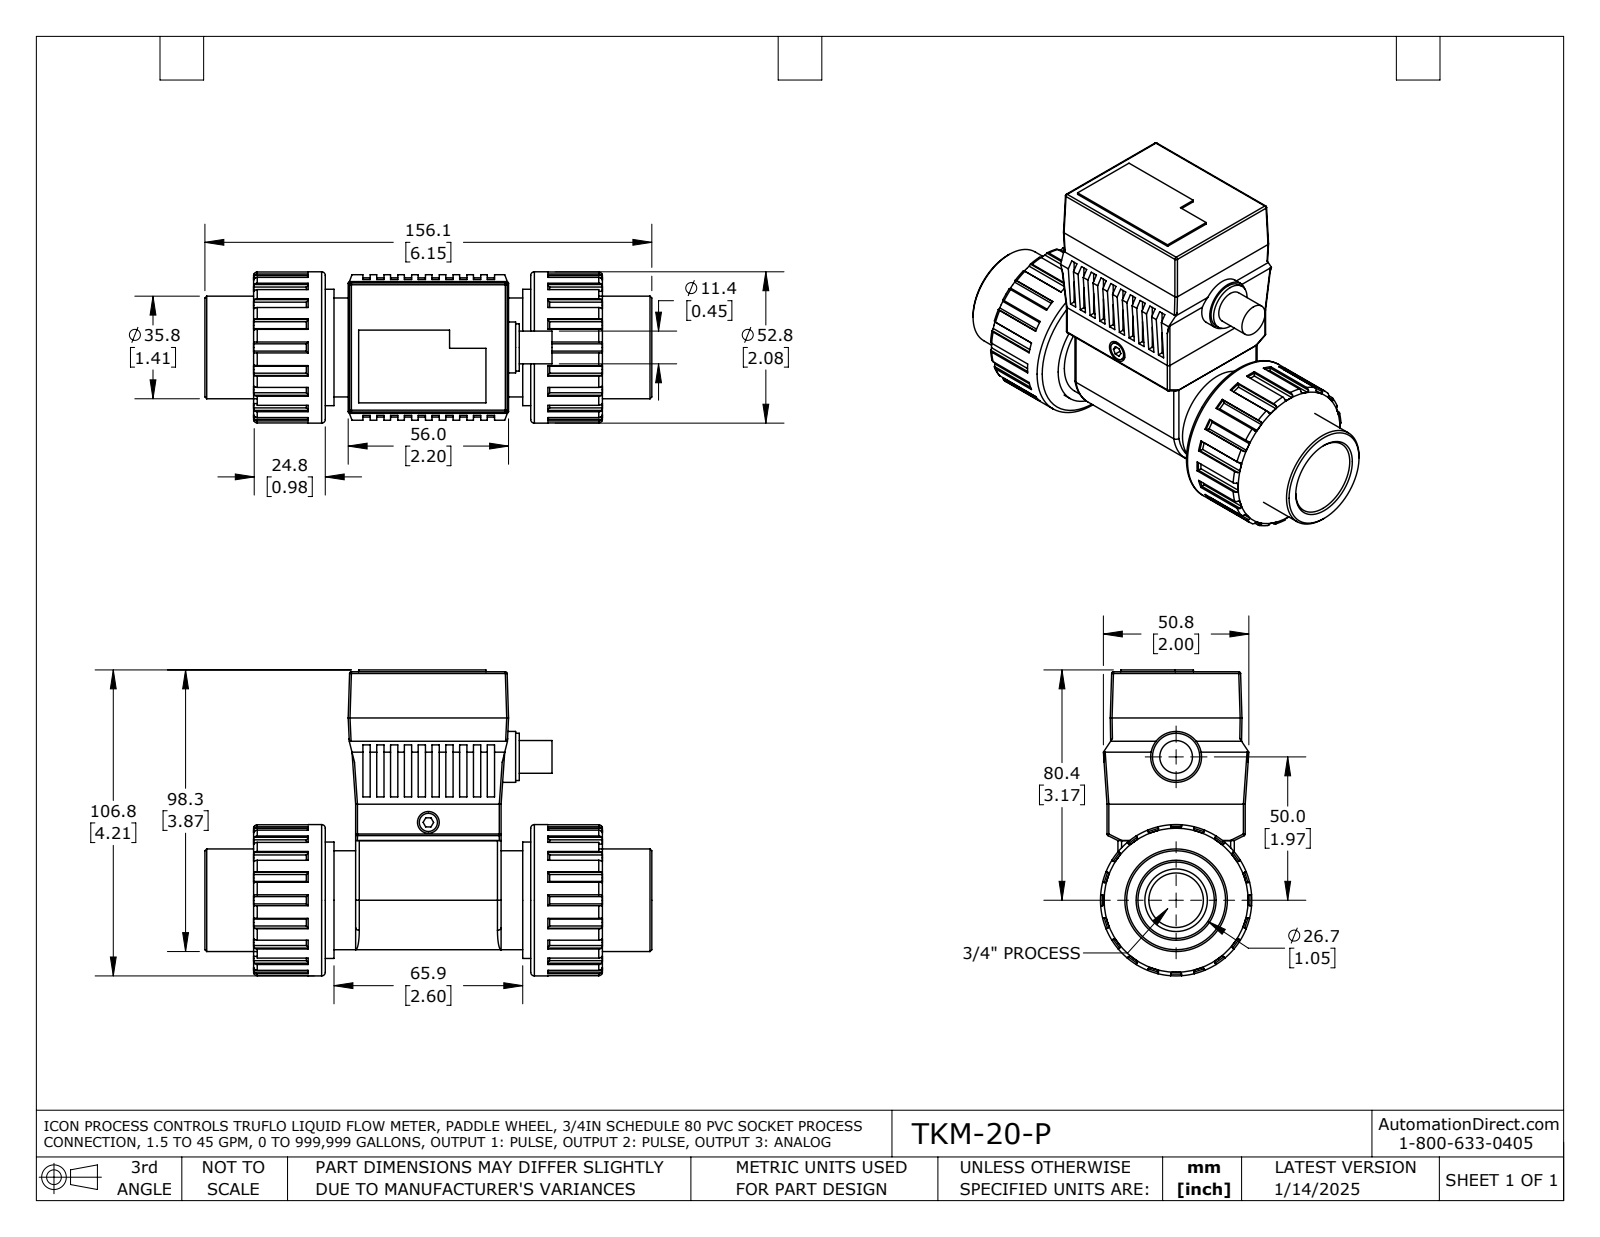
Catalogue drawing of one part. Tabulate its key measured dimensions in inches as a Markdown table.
| quantity | value |
| --- | --- |
| part name | TKM-20-P |
| STEP written by | SolidWorks 2021 (AUTOMOTIVE_DESIGN) |
| units | inches |
| bodies | 9 solids, 711 faces (356 planar, 247 cylindrical, 108 other) |
| overall size | 6.145 × 4.205 × 2.08 |
| volume | 19.73 in³ |
| surface area | 125.5 in² |
| round holes (diameter × count) | 0.128 × 4, 0.3 × 1, 0.75 × 1, 0.86 × 1, 1.05 × 1, 1.1 × 1, 1.2 × 1, 1.25 × 1, 1.4 × 1, 1.445 × 1 |
| round bosses / shafts (diameter × count) | 2.08 × 1, 1.6 × 1, 1.53 × 1, 1.41 × 1, 1.36 × 1, 1.1 × 1, 1.024 × 1, 0.7 × 1 |
| partial cylindrical surfaces (radius × count) | 0.025 × 106, 0.05 × 4, 0.465 × 1, 0.512 × 1, 0.811 × 1 |
| main face-to-face distances | 0.957, 2.957, 0.15, 3.915, 2.32, 1.775, 0.025, 2.345, 1.6, 0.446 |
| hole center spacings | 0.979, 1.181, 1.561, 0.979, 1.957, 1.958 |
